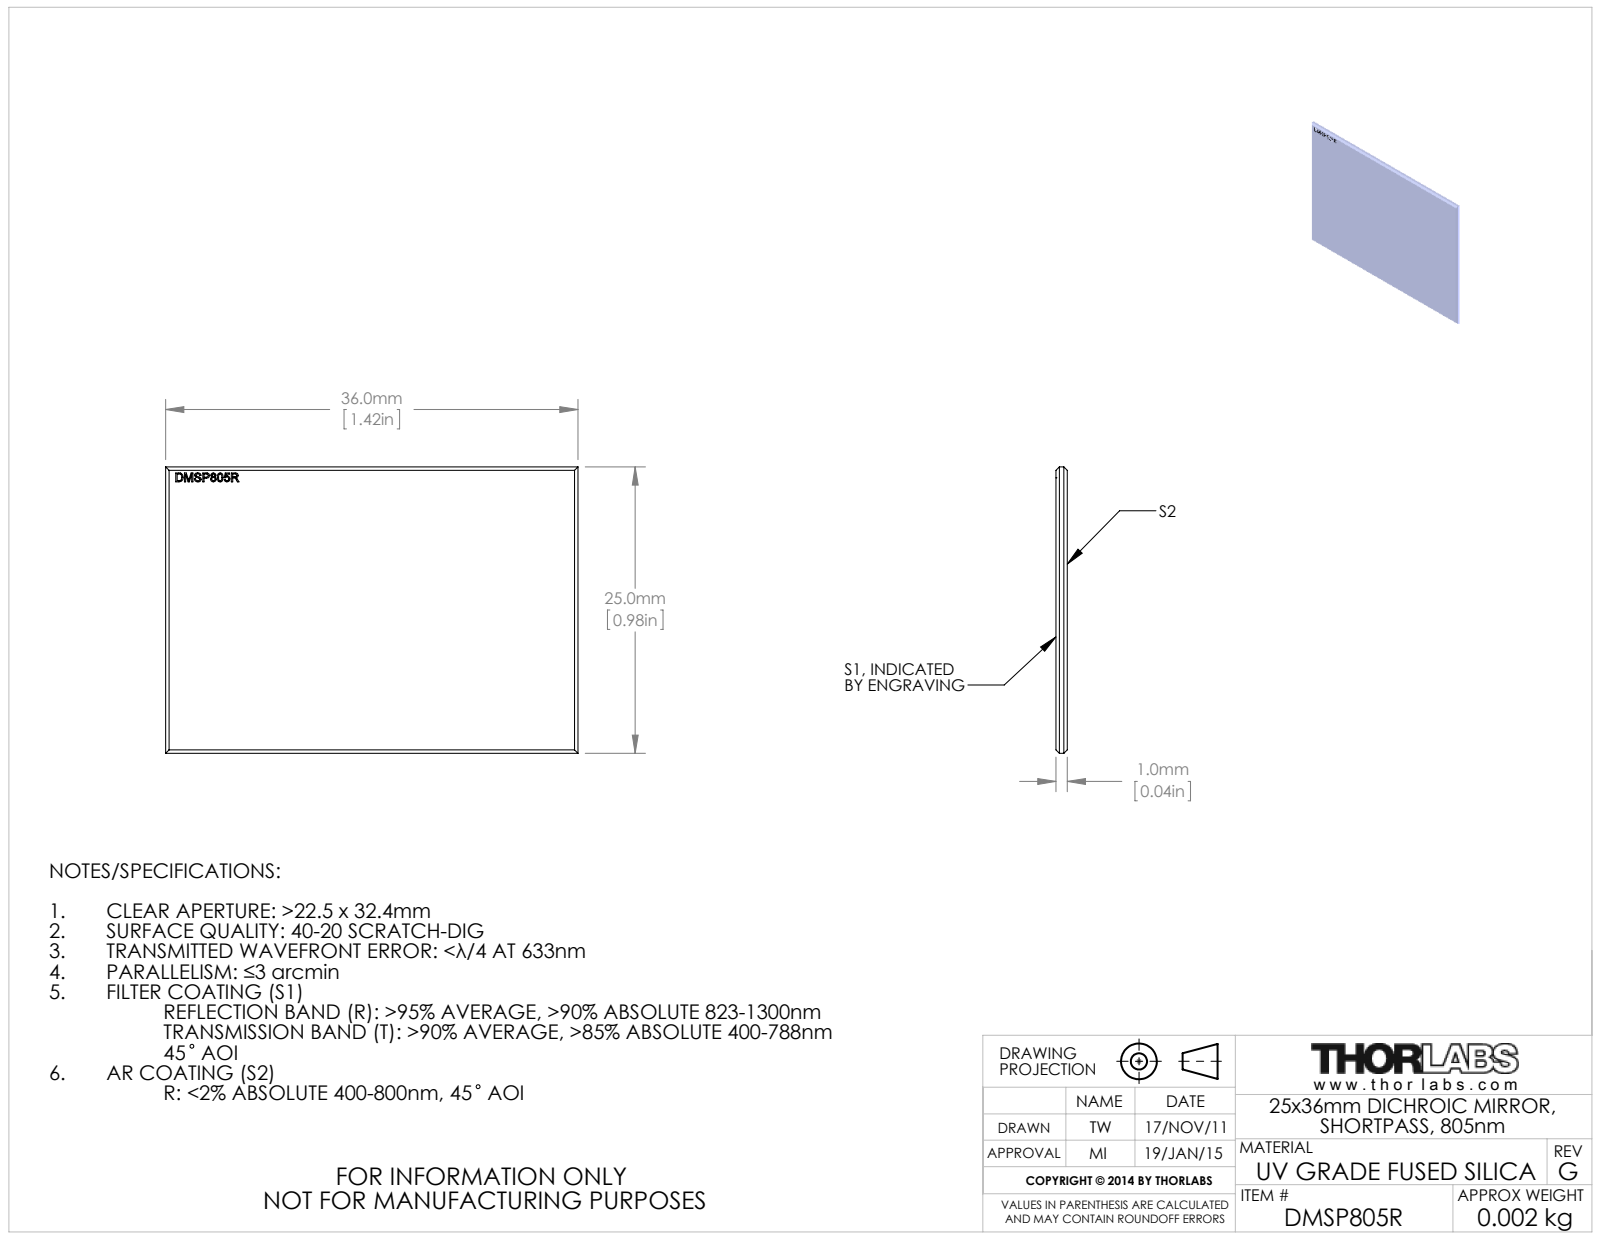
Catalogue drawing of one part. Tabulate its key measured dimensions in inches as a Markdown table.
| quantity | value |
| --- | --- |
| part name | 21946-E0W |
| STEP written by | SolidWorks 2011 (CONFIG_CONTROL_DESIGN) |
| units | inches |
| bodies | 0 solids, 44 faces (35 planar, 0 cylindrical, 9 other) |
| overall size | 1.417 × 0.984 × 0.039 |
| main face-to-face distances | 0.039, 0.707, 0.707, 0.984, 1.013, 1.013, 1.417, 0.039, 0.065, 1.353 |
